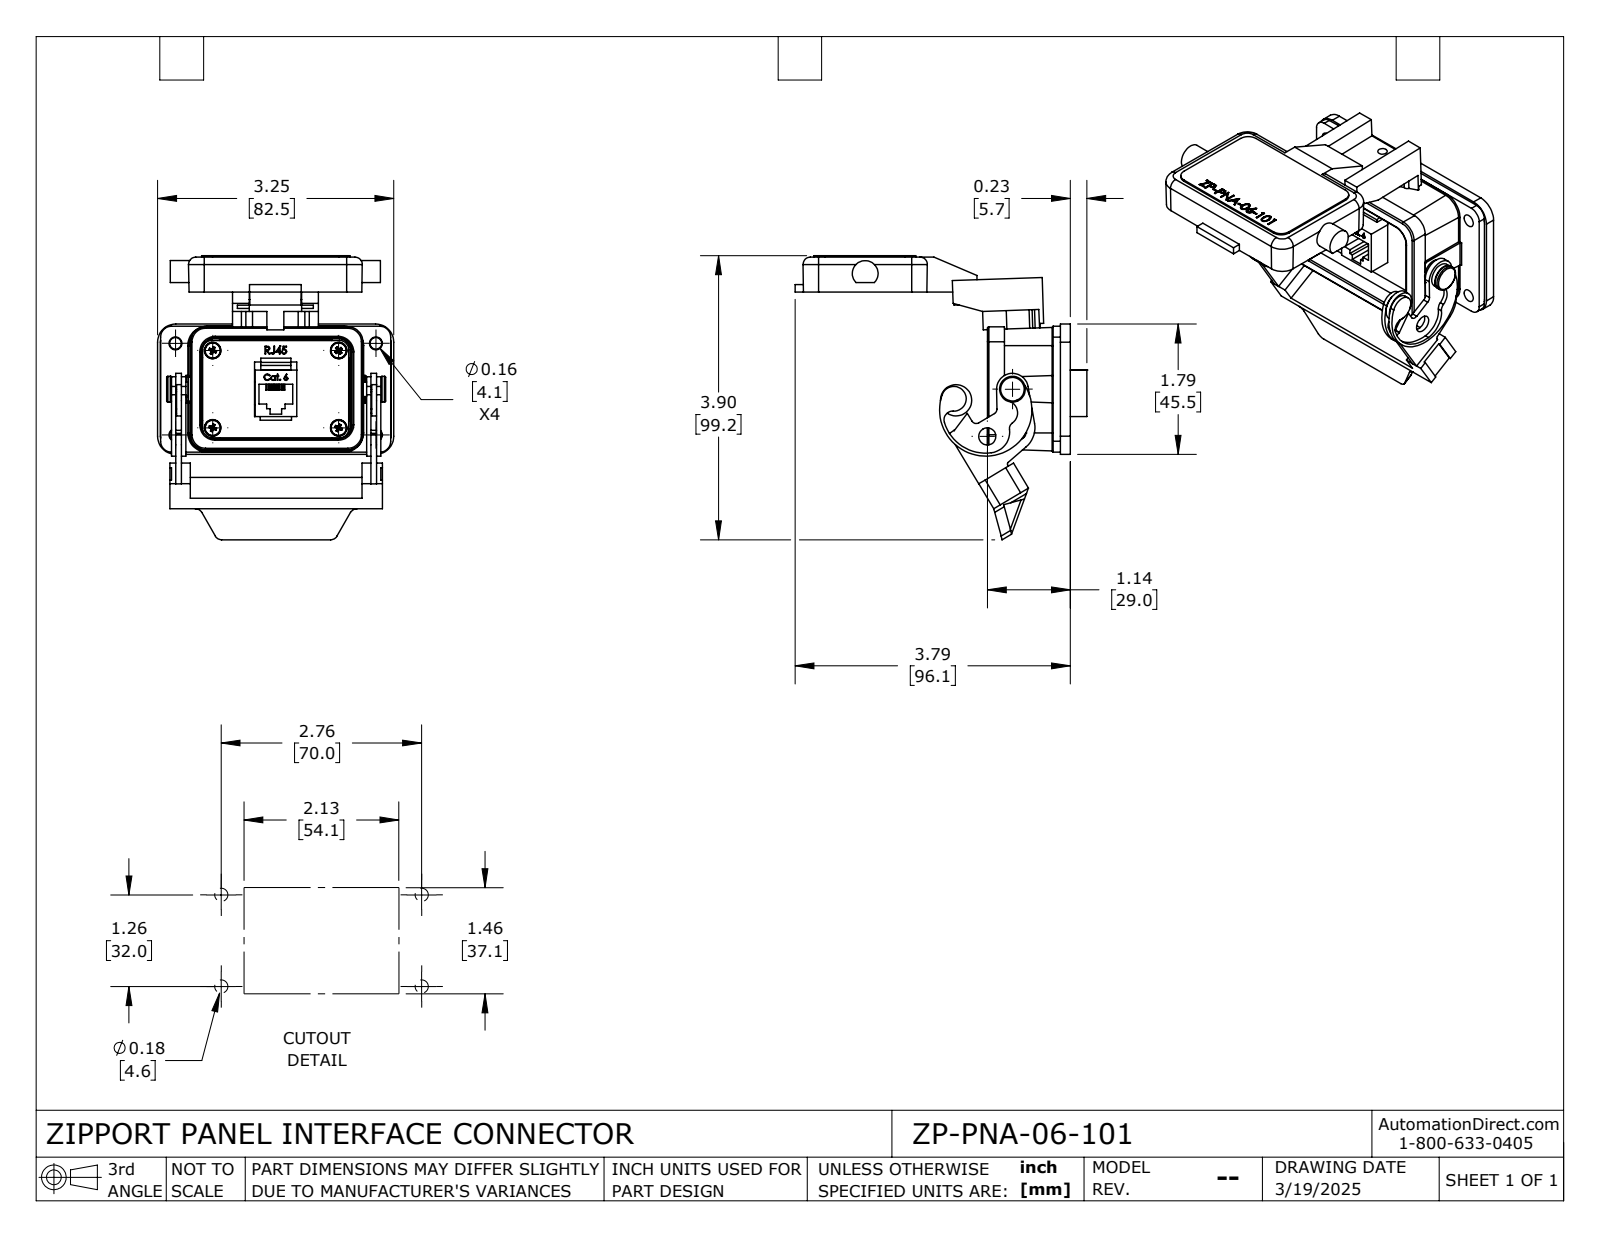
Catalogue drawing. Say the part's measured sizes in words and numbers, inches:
The part is named "ZP-PNA-06-101". Its 3-D file was written by "SolidWorks 2024 (CONFIG_CONTROL_DESIGN)". It is 1 solid with 1165 faces: 686 planar, 299 cylindrical and 180 other. Overall it measures 4.011 by 3.904 by 3.248 inches. Its volume is 4.314 cubic inches and its surface area 77.34 square inches. Round holes: 4 of diameter 0.098, 4 of diameter 0.144, 4 of diameter 0.16, 4 of diameter 0.177, 2 of diameter 0.12, 2 of diameter 0.202, 1 of diameter 0.13, 1 of diameter 0.133, 1 of diameter 0.157, 1 of diameter 0.163, 1 of diameter 0.2, 1 of diameter 0.236. Round bosses or shafts: 4 of diameter 0.226, 4 of diameter 0.22, 4 of diameter 0.118, 1 of diameter 0.43, 1 of diameter 0.354, 1 of diameter 0.238, 1 of diameter 0.237, 1 of diameter 0.204. Partial cylindrical surfaces (rounded edges, fillets, slot ends): 16 of radius 0.1, 12 of radius 0.15, 8 of radius 0.02, 8 of radius 0.025, 7 of radius 0.015, 4 of radius 0.035, 4 of radius 0.093, 4 of radius 0.094. The main face-to-face distances are 0.06, 0.135, 0.665, 0.724, 0.137, 1.589, 0.487, 0.237, 0.427, 1.526. The hole center spacings are 0.521, 1.269, 2.246, 2.527, 1.063, 1.26, 1.732, 2.032.
